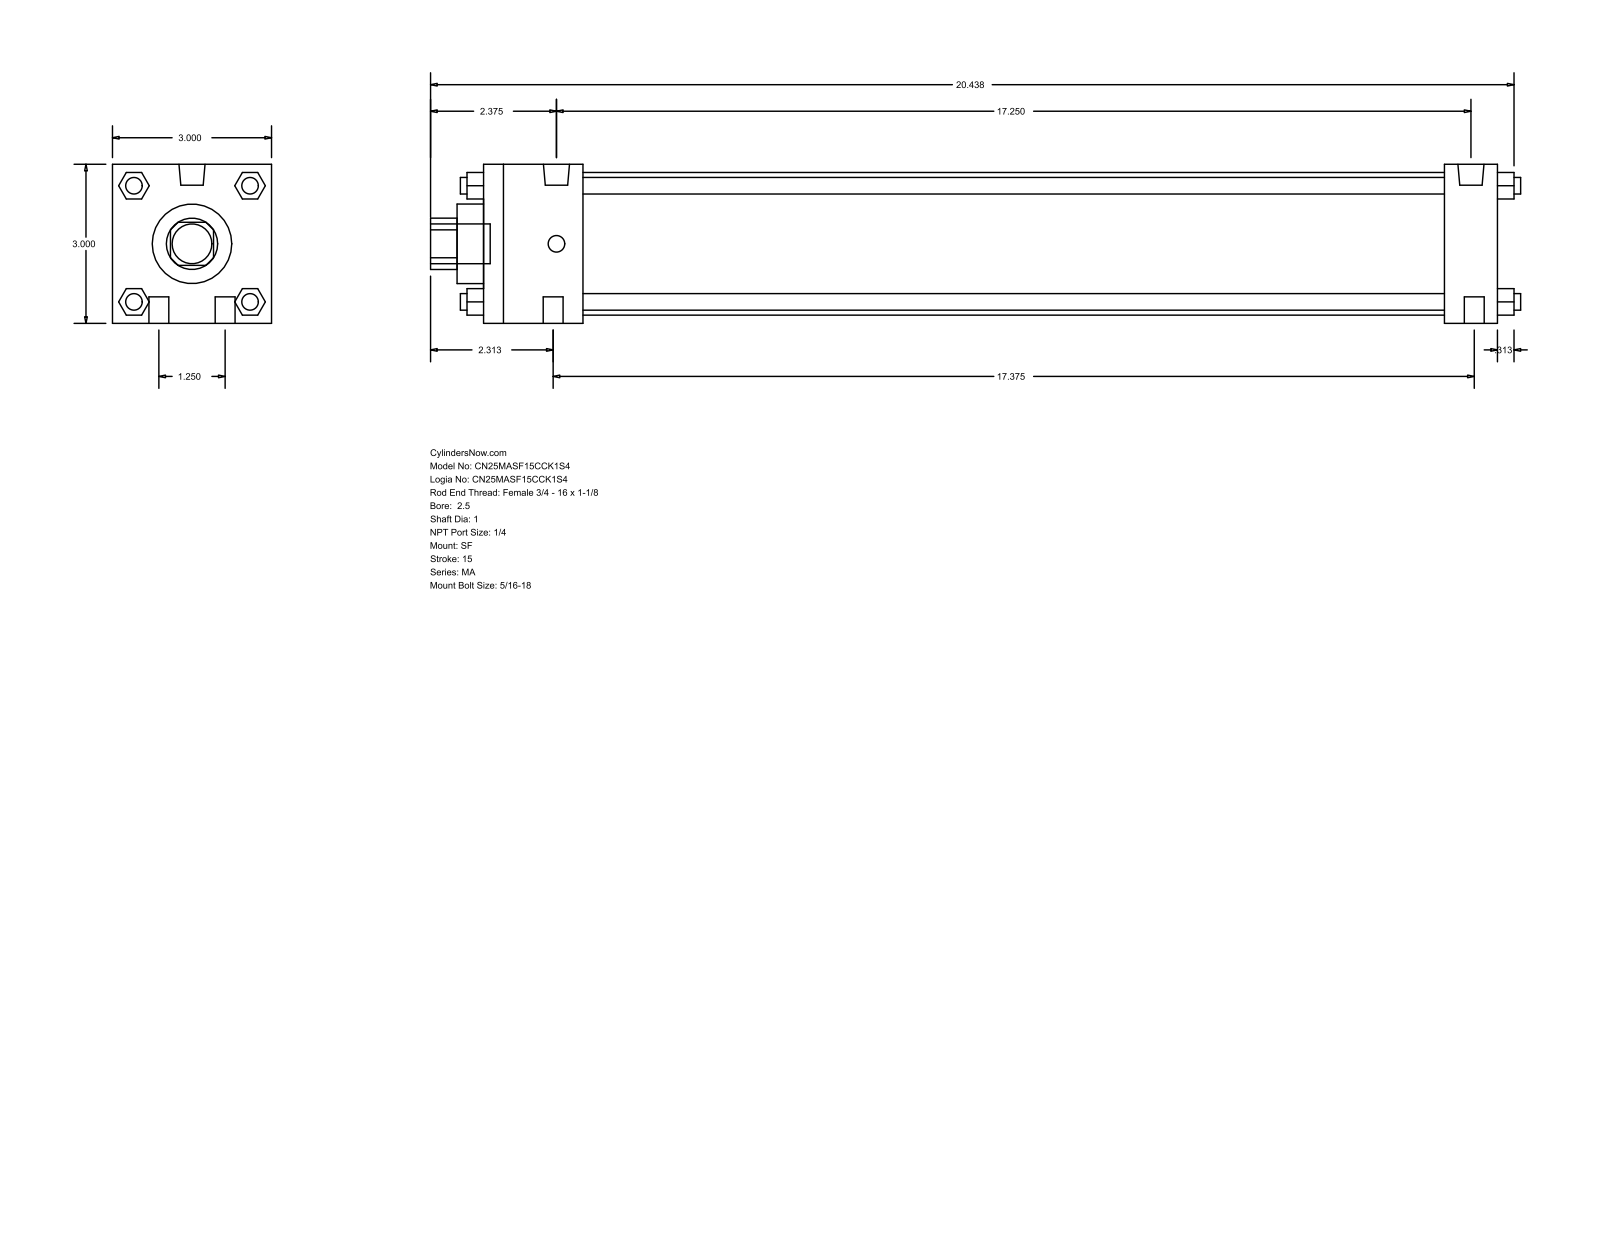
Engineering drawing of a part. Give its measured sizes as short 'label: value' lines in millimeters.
name: MA_SF__0250_1
written by: GSSL Pune (CONFIG_CONTROL_DESIGN)
unit: mm
bodies: 0 solids, 124 faces (94 planar, 30 cylindrical, 0 other)
size: 522.29 × 76.2 × 76.2
holes: 1× ⌀25.4, 1× ⌀38.1, 1× ⌀68.33
bosses: 6× ⌀7.94, 4× ⌀9.53, 2× ⌀12.49, 1× ⌀19.05
rounds: 1× R12.29
face distances: 76.2, 485.78, 12.7, 460.37, 25.41, 47.63, 412.74, 438.15, 27.81, 48.17
